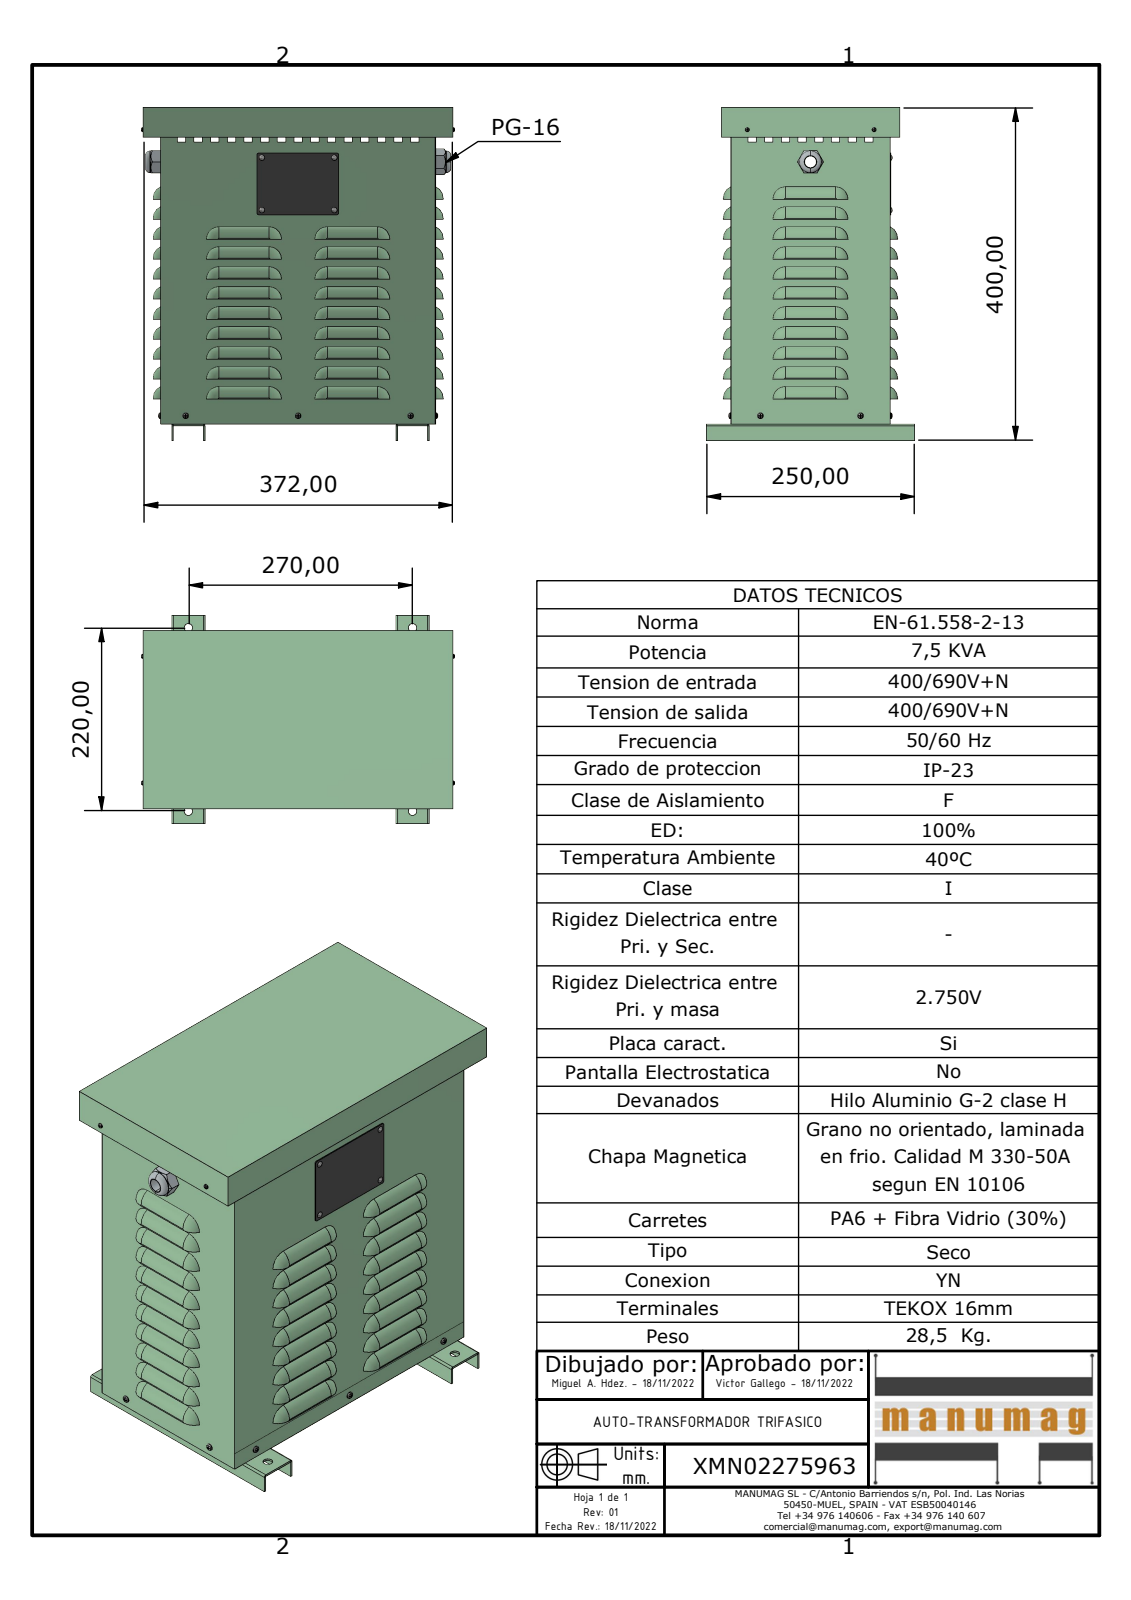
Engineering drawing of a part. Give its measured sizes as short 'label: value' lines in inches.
name: XMN02275963; JE010 NACIONAL CUERPO; JE010 NACIONAL BASE; PLACA CARACTERISTICAS (+6 more)
written by: Autodesk Inventor 2023 (AUTOMOTIVE_DESIGN)
unit: in
bodies: 26 solids, 1888 faces (958 planar, 396 cylindrical, 534 other)
size: 15.773 × 14.809 × 9.843
volume: 53.89 in³; area: 2 086 in²
holes: 9× ⌀0.157, 4× ⌀0.118, 4× ⌀0.394, 1× ⌀0.551, 1× ⌀0.945
bosses: 5× ⌀0.138, 5× ⌀0.125, 4× ⌀0.126, 2× ⌀0.098, 2× ⌀0.089, 1× ⌀1.024, 1× ⌀0.906, 1× ⌀0.886
rounds: 66× R0.551, 42× R0.276, 42× R0.591, 12× R0.059, 8× R0.197, 8× R0.217, 5× R0.02, 4× R0.02
face distances: 0.02, 7.5, 0.059, 7.48, 14.926, 12.972, 7.52, 14.985, 12.953, 12.992
hole spacings: 2.48, 3.356, 3.425, 4.229, 5.315, 5.984, 8.661, 9.874
